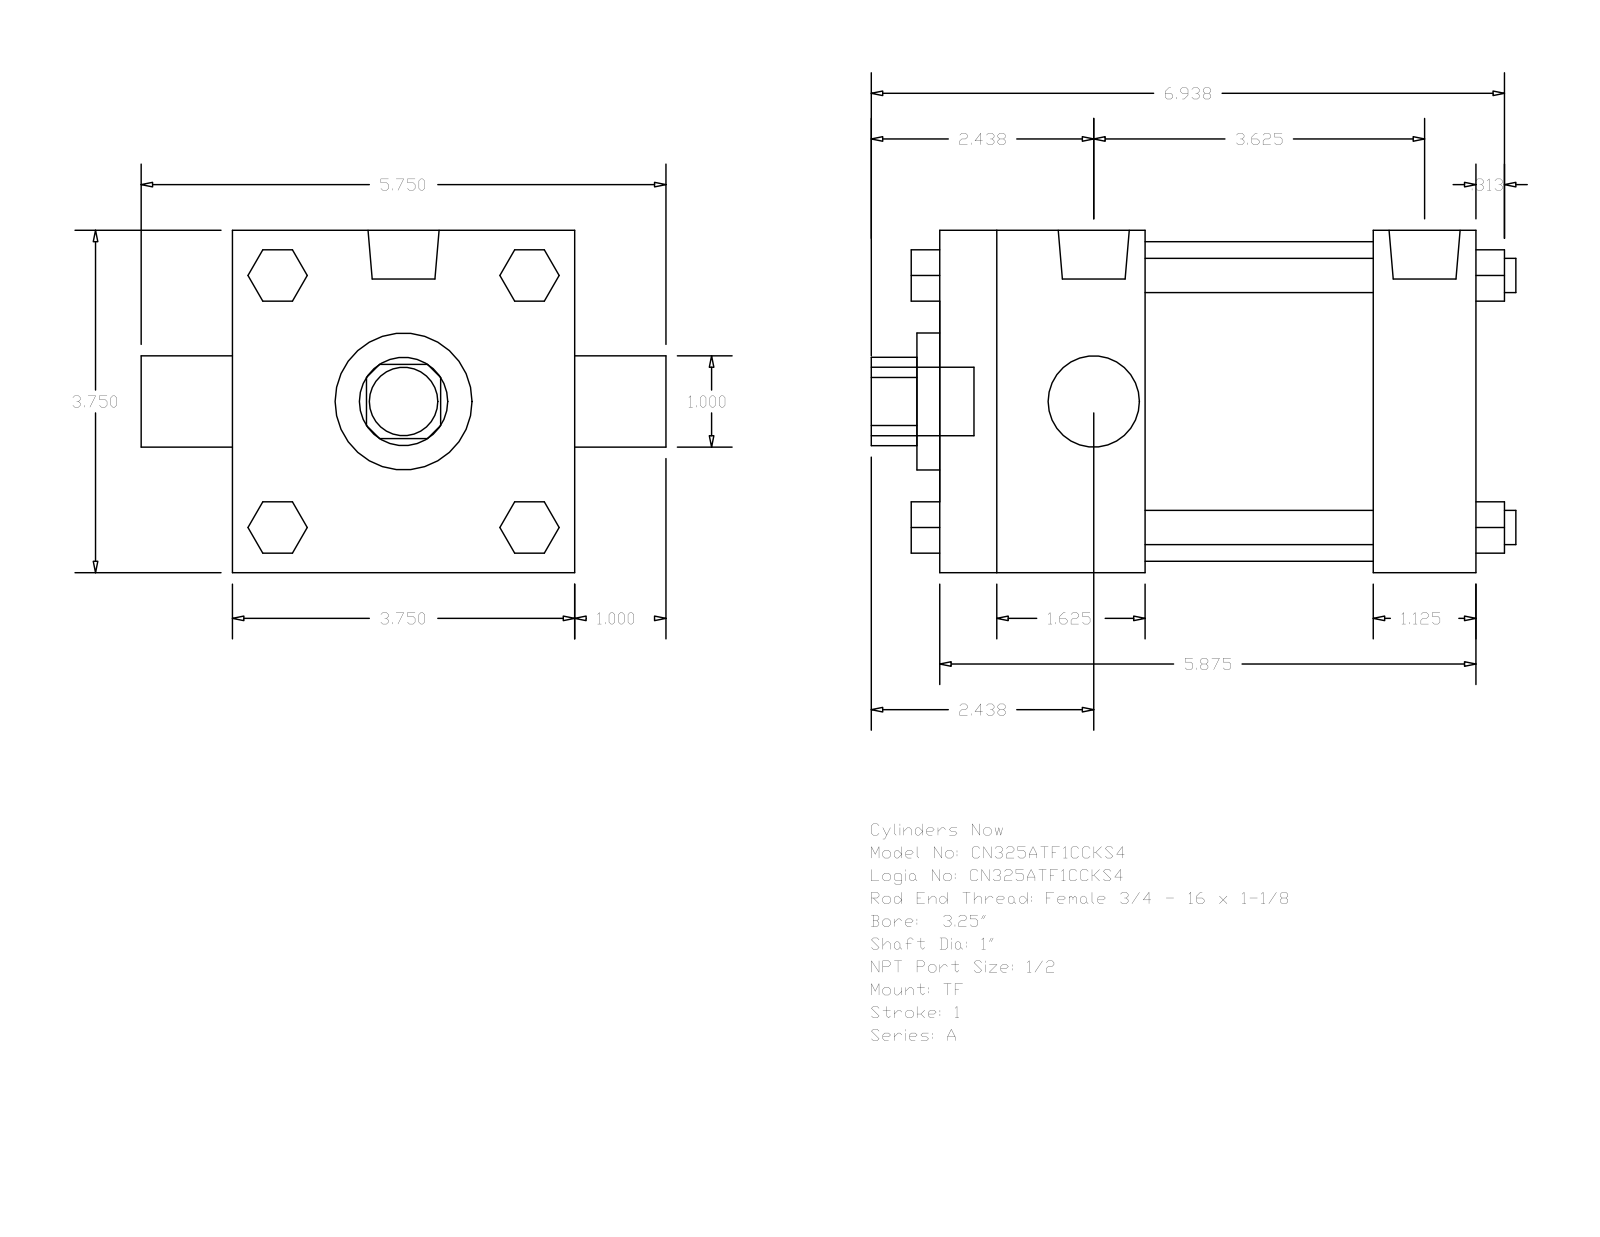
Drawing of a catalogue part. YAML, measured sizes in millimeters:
part_name: "A_TF__0325_1"
step_written_by: "GSSL Pune (CONFIG_CONTROL_DESIGN)"
units: millimeters
bodies: {solids: 0, faces: 120, planar: 92, cylindrical: 28, other: 0}
overall_size: [179.39, 146.05, 95.25]
round_holes:
  - {diameter: 25.4, count: 2}
  - {diameter: 38.1, count: 1}
  - {diameter: 88.9, count: 1}
round_bosses_or_shafts:
  - {diameter: 9.53, count: 4}
  - {diameter: 8.73, count: 3}
  - {diameter: 19.77, count: 2}
  - {diameter: 19.05, count: 1}
partial_cylinders:
  - {radius: 12.29, count: 1}
face_to_face_distances: [95.24, 149.23, 120.65, 63.5, 57.15, 92.08, 28.58, 14.28, 35.05, 60.71]
